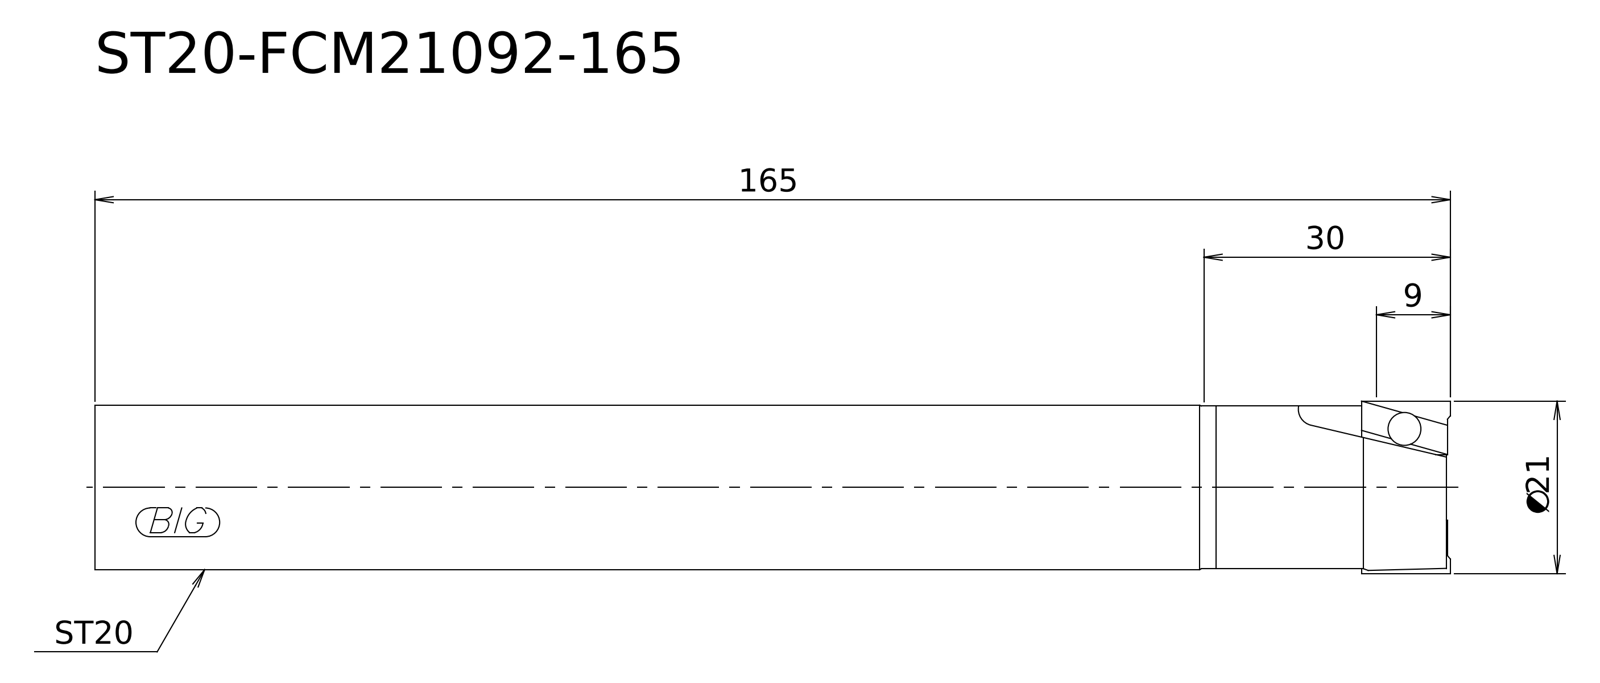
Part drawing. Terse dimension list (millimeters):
written by: Kubotek KeyCreator V8.5.1 (14335) (CONFIG_CONTROL_DESIGN)
unit: mm
bodies: 1 solid, 7 faces (3 planar, 3 cylindrical, 1 other)
size: 165 × 21 × 21
volume: 52 062 mm³; area: 11 090 mm²
bosses: 1× ⌀21, 1× ⌀20, 1× ⌀19.8
face distances: 165, 10.81, 154.19
